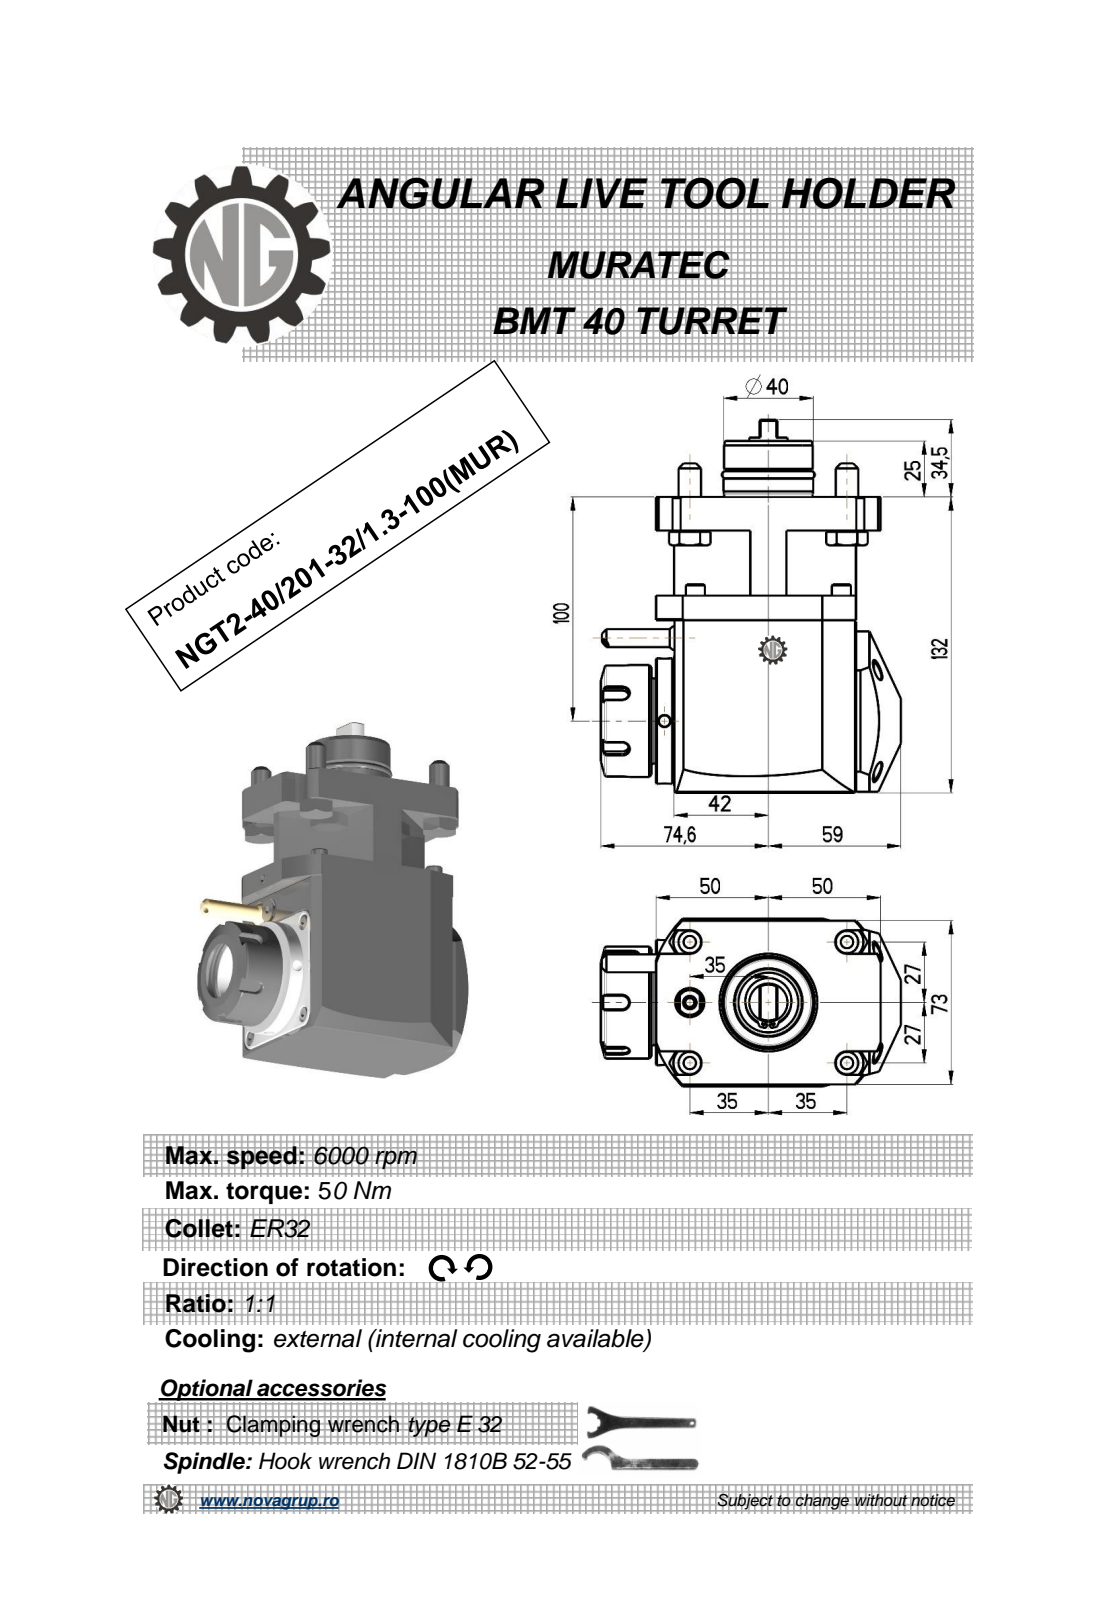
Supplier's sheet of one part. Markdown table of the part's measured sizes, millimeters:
| quantity | value |
| --- | --- |
| part name | NGT2_40_201_32_1_3_100_MUR |
| STEP written by | PRO/ENGINEER BY PARAMETRIC TECHNOLOGY CORPORATION, 2010280 (CONFIG_CONTROL_DESIGN) |
| units | millimeters |
| bodies | 2 solids, 412 faces (177 planar, 84 cylindrical, 151 other) |
| overall size | 166.5 × 133.6 × 75 |
| volume | 900 161 mm³ |
| surface area | 81 446 mm² |
| round holes (diameter × count) | 5 × 3, 3 × 1, 4.2 × 1, 27 × 1 |
| round bosses / shafts (diameter × count) | 14.6 × 4, 10 × 4, 56 × 1, 50 × 1, 43 × 1, 41 × 1, 40 × 1, 39.5 × 1 |
| partial cylindrical surfaces (radius × count) | 0.22 × 6, 3 × 5, 5.25 × 4, 6 × 1, 40 × 1, 53.5 × 1 |
| main face-to-face distances | 132, 75, 1, 74, 44, 88, 63, 15, 29, 117 |
| hole center spacings | 11.25, 40.93 |
